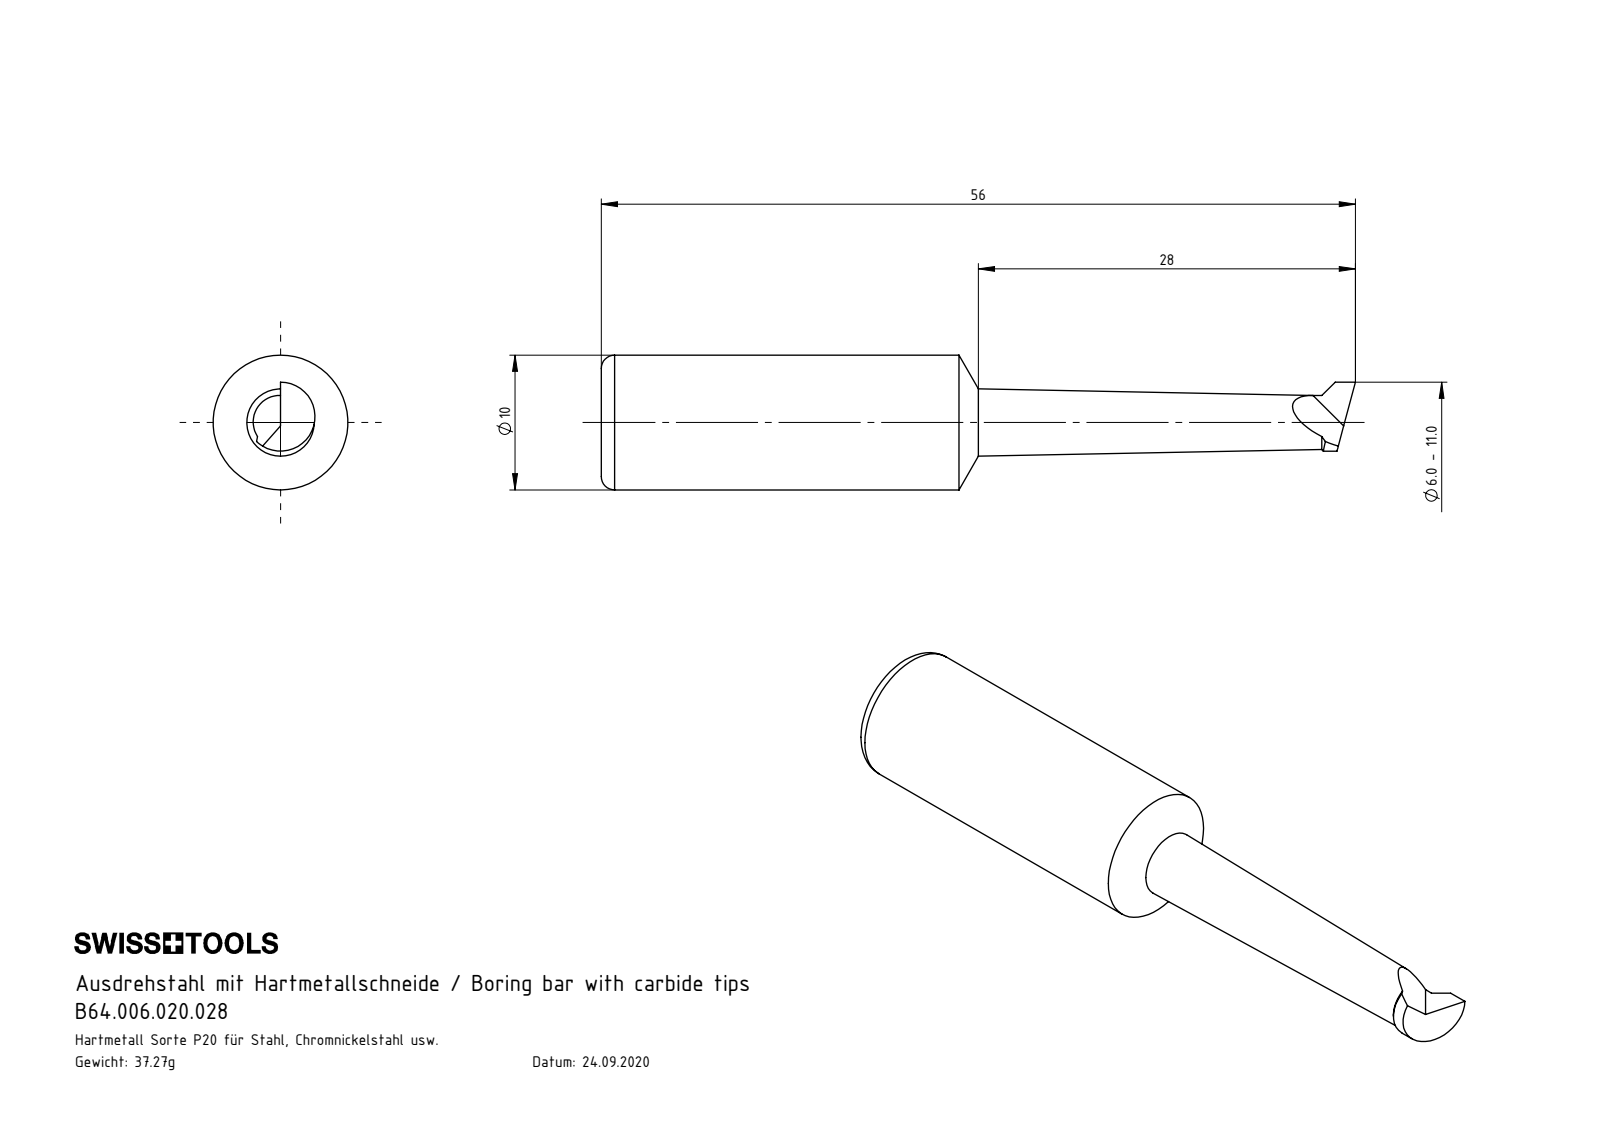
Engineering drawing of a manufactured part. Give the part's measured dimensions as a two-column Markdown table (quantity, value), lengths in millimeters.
| quantity | value |
| --- | --- |
| part name | B64.006.020.028 |
| STEP written by | SolidWorks 2022 (CONFIG_CONTROL_DESIGN) |
| units | millimeters |
| bodies | 1 solid, 14 faces (4 planar, 3 cylindrical, 7 other) |
| overall size | 56 × 10 × 10 |
| volume | 2 570 mm³ |
| surface area | 1 367 mm² |
| round bosses / shafts (diameter × count) | 10 × 1 |
| partial cylindrical surfaces (radius × count) | 2.56 × 1 |
